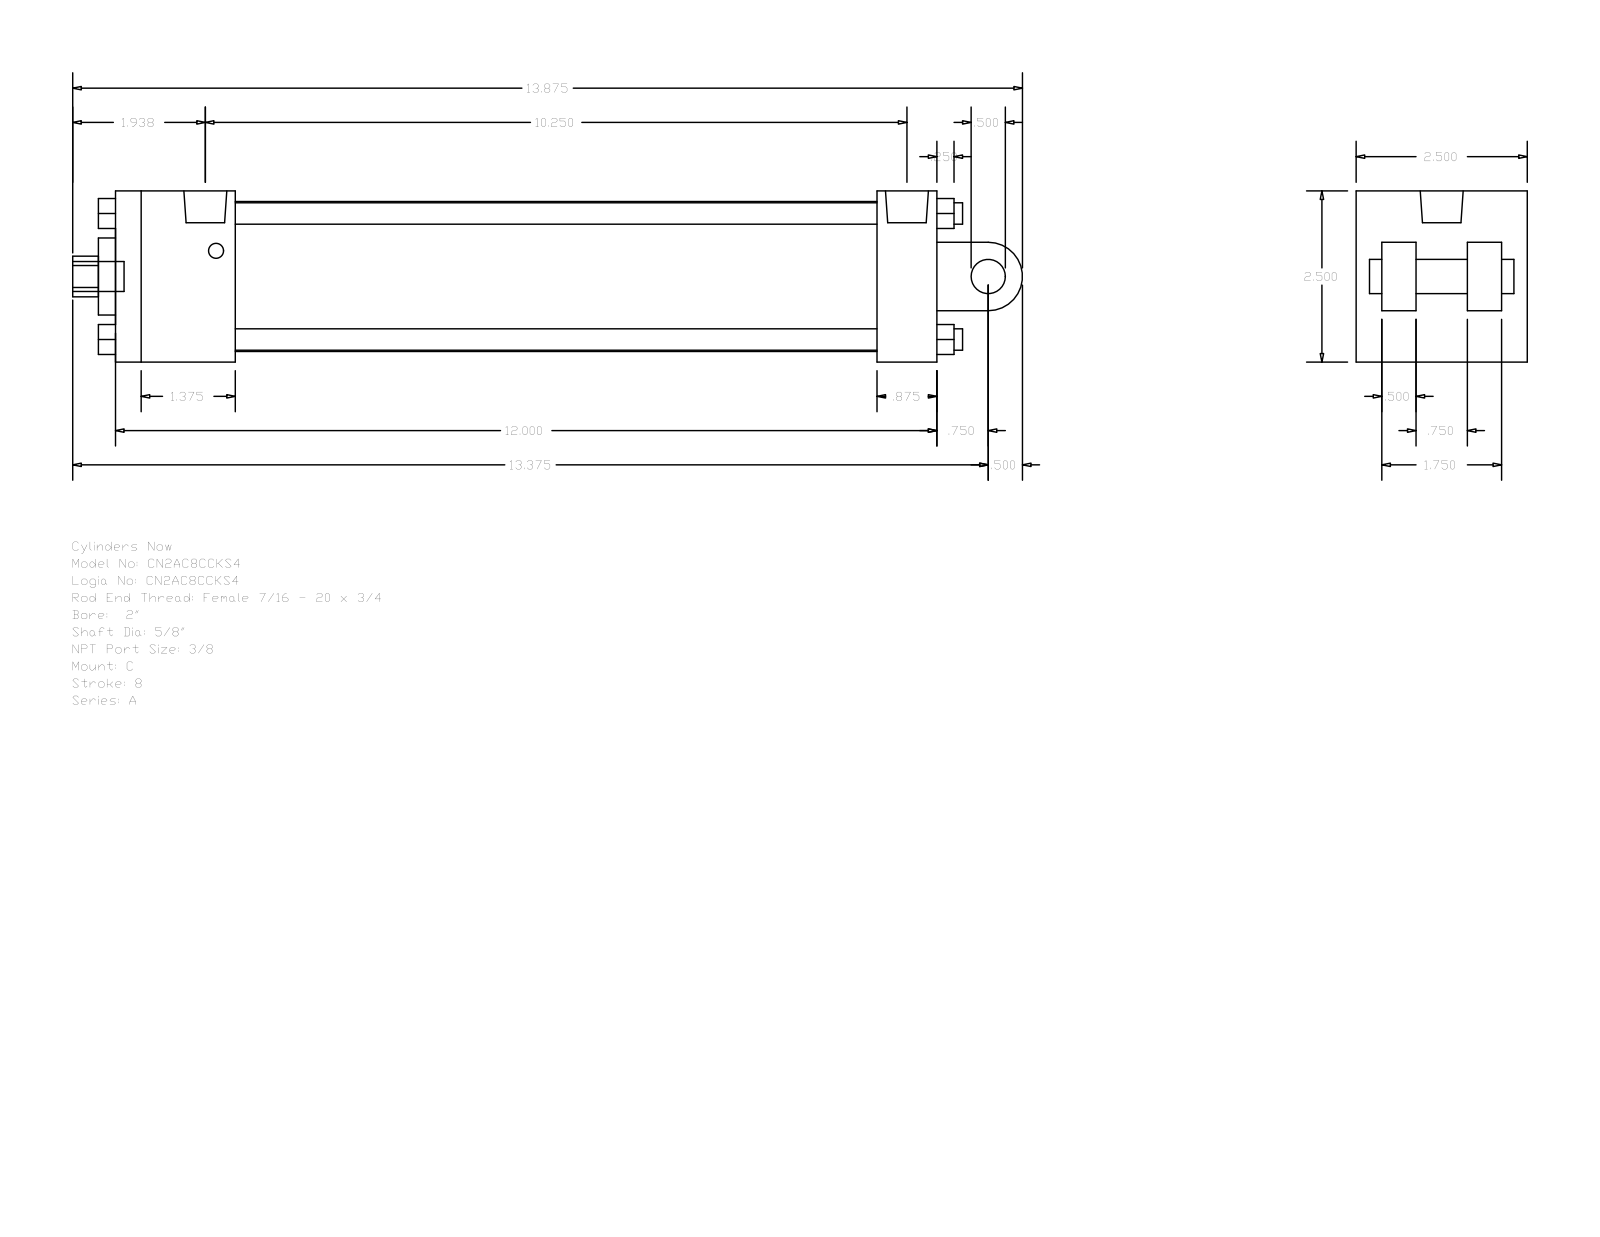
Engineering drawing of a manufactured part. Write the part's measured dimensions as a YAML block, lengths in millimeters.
part_name: "A_C__0200_0.625"
step_written_by: "GSSL Pune (CONFIG_CONTROL_DESIGN)"
units: millimeters
bodies: {solids: 0, faces: 135, planar: 102, cylindrical: 33, other: 0}
overall_size: [352.43, 63.5, 63.5]
round_holes:
  - {diameter: 5.56, count: 2}
  - {diameter: 15.88, count: 1}
  - {diameter: 15.93, count: 1}
  - {diameter: 28.57, count: 1}
  - {diameter: 55.63, count: 1}
round_bosses_or_shafts:
  - {diameter: 7.94, count: 4}
  - {diameter: 5.56, count: 2}
  - {diameter: 15.93, count: 1}
  - {diameter: 12.7, count: 1}
  - {diameter: 11.11, count: 1}
partial_cylinders:
  - {radius: 7.54, count: 1}
  - {radius: 12.7, count: 1}
face_to_face_distances: [63.5, 304.8, 44.45, 9.52, 260.35, 282.57, 238.12, 22.23, 12.7, 41.28]
hole_center_spacings: [3.97]
